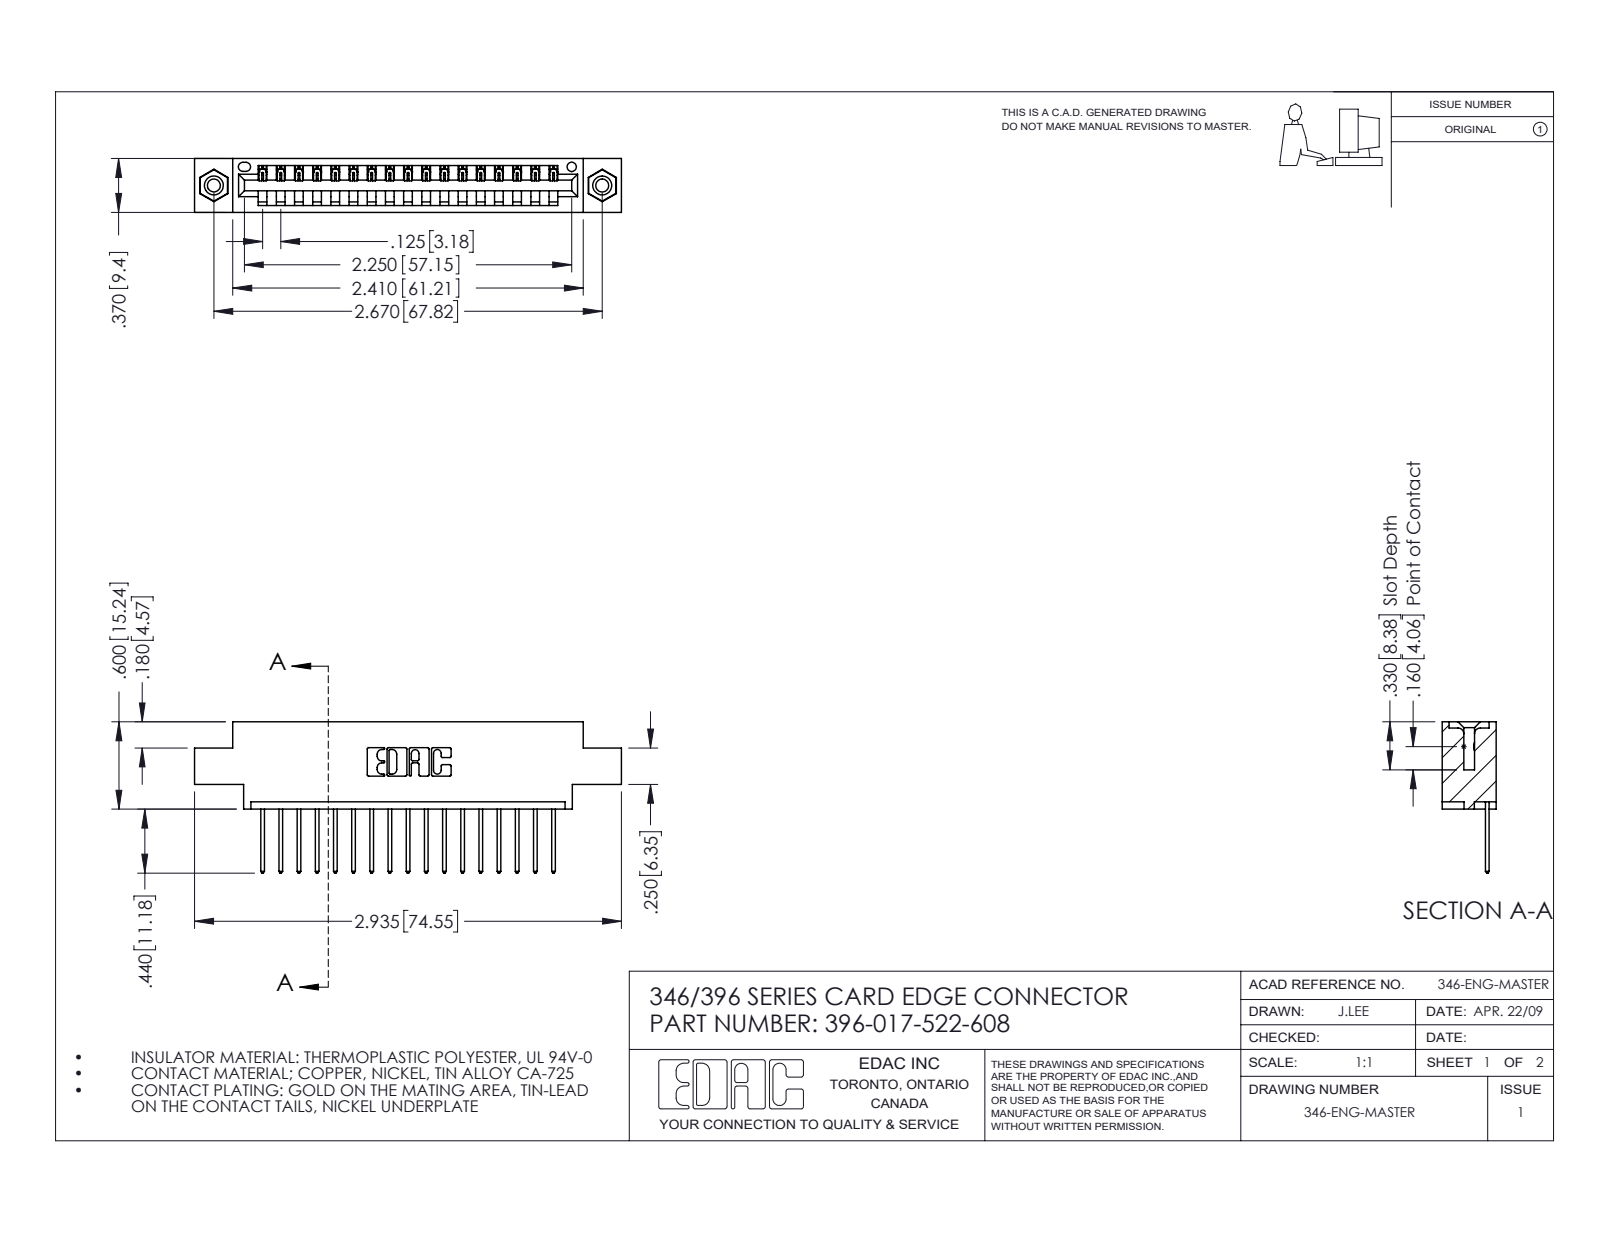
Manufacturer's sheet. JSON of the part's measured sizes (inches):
{"part_name": "345-250-001_345-250-003-102; 345-292-001_345-293-122; 346 Part_0.170 Offset - 0.156 Dia-TI; 396-017-522-608", "step_written_by": "SolidWorks 2016 (CONFIG_CONTROL_DESIGN)", "units": "inches", "bodies": {"solids": 20, "faces": 1172, "planar": 792, "cylindrical": 364, "other": 16}, "overall_size": [2.935, 1.04, 0.37], "volume_in3": 0.415, "surface_area_in2": 13.14, "round_holes": [[0.089, 2], [0.125, 2], [0.156, 2], [0.064, 1]], "round_bosses_or_shafts": [[0.155, 2]], "partial_cylinders_radius": [[0.006, 34], [0.01, 34], [0.01, 22], [0.007, 6], [0.031, 6], [0.026, 3], [0.031, 2], [0.04, 2]], "face_to_face_distances": [0.048, 0.322, 0.37, 0.25, 0.072, 0.298, 0.025, 0.222, 0.148, 0.1], "hole_center_spacings": [0.246, 2.463, 2.67]}
